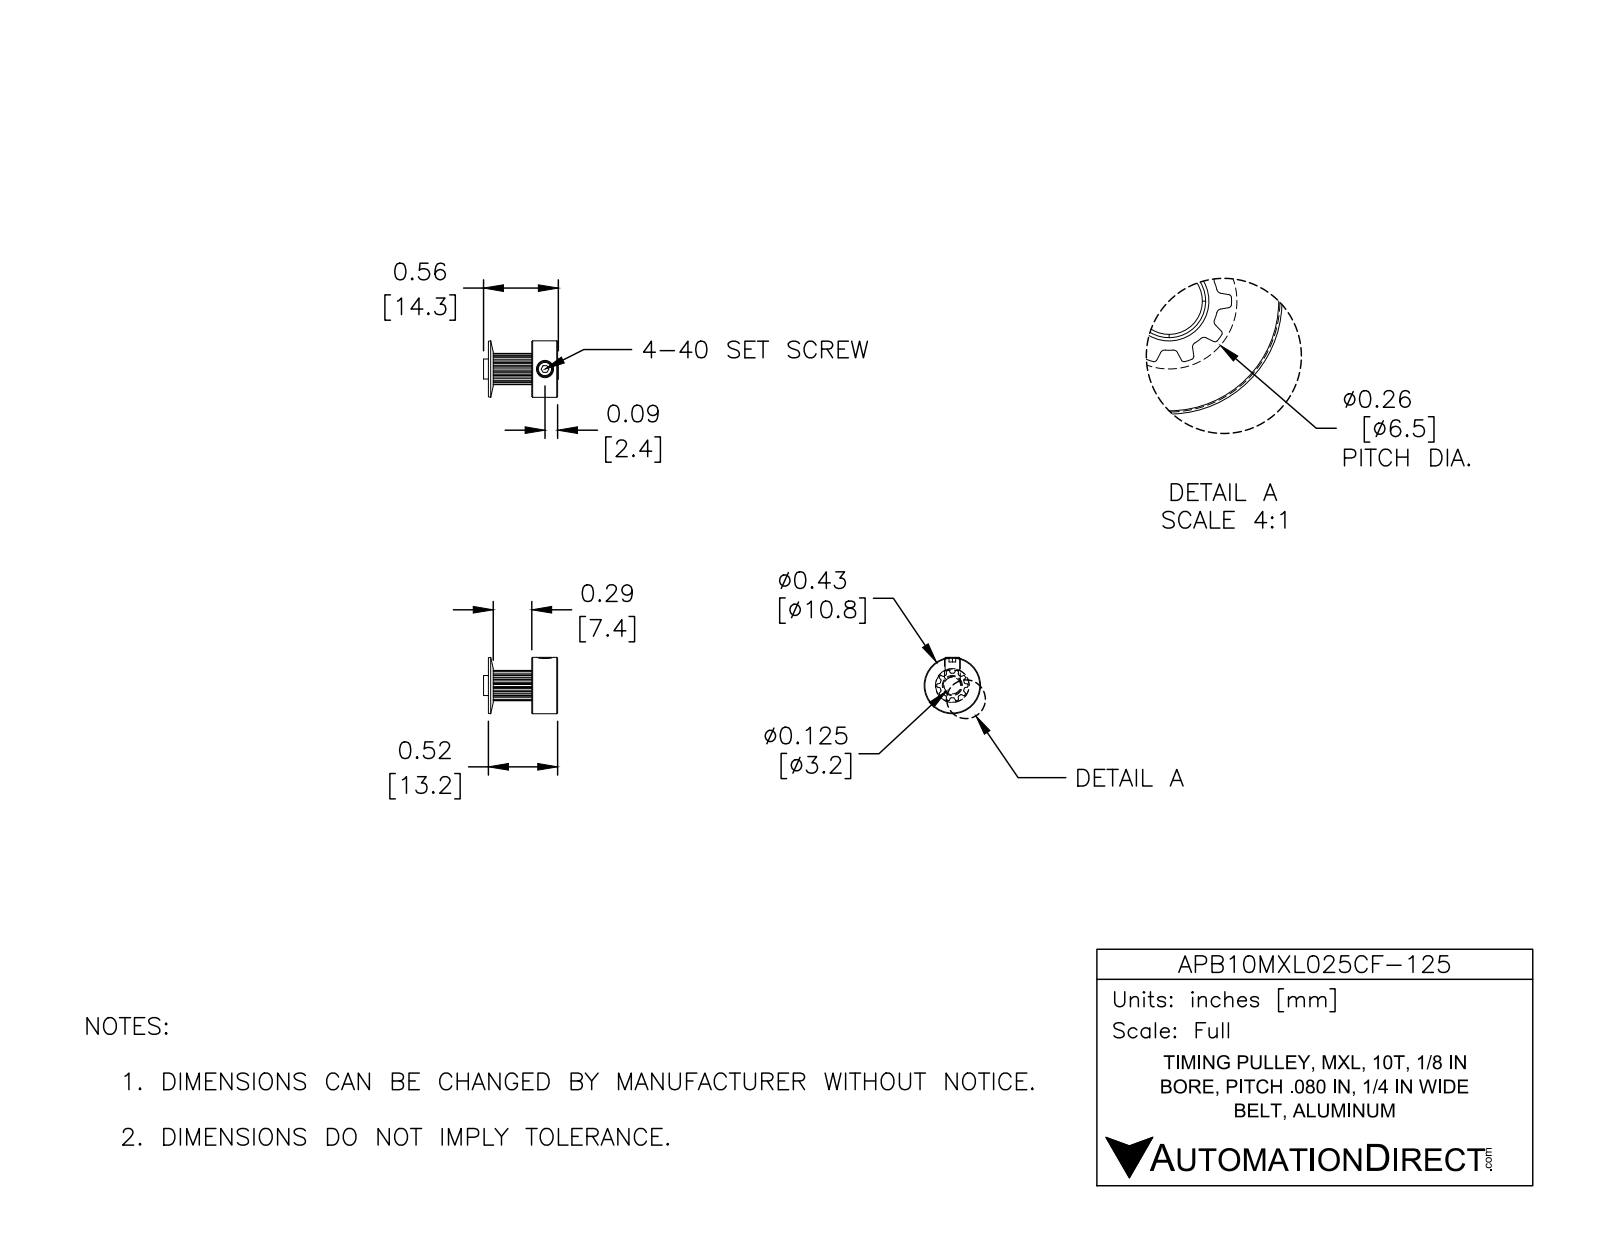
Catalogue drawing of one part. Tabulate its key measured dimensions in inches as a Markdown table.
| quantity | value |
| --- | --- |
| part name | APB10MXL025CF-125 |
| STEP written by | SolidWorks 2016 (AUTOMOTIVE_DESIGN) |
| units | inches |
| bodies | 2 solids, 134 faces (35 planar, 81 cylindrical, 18 other) |
| overall size | 0.563 × 0.425 × 0.425 |
| volume | 0.033 in³ |
| surface area | 1.365 in² |
| round holes (diameter × count) | 0.118 × 1, 0.125 × 1 |
| round bosses / shafts (diameter × count) | 0.425 × 1, 0.15 × 1, 0.11 × 1 |
| partial cylindrical surfaces (radius × count) | 0.005 × 20, 0.009 × 20, 0.092 × 1, 0.117 × 1 |
| main face-to-face distances | 0.194, 0.063, 0.309, 0.504, 0.019, 0.29, 0.485, 0.098, 0.054, 0.073 |
